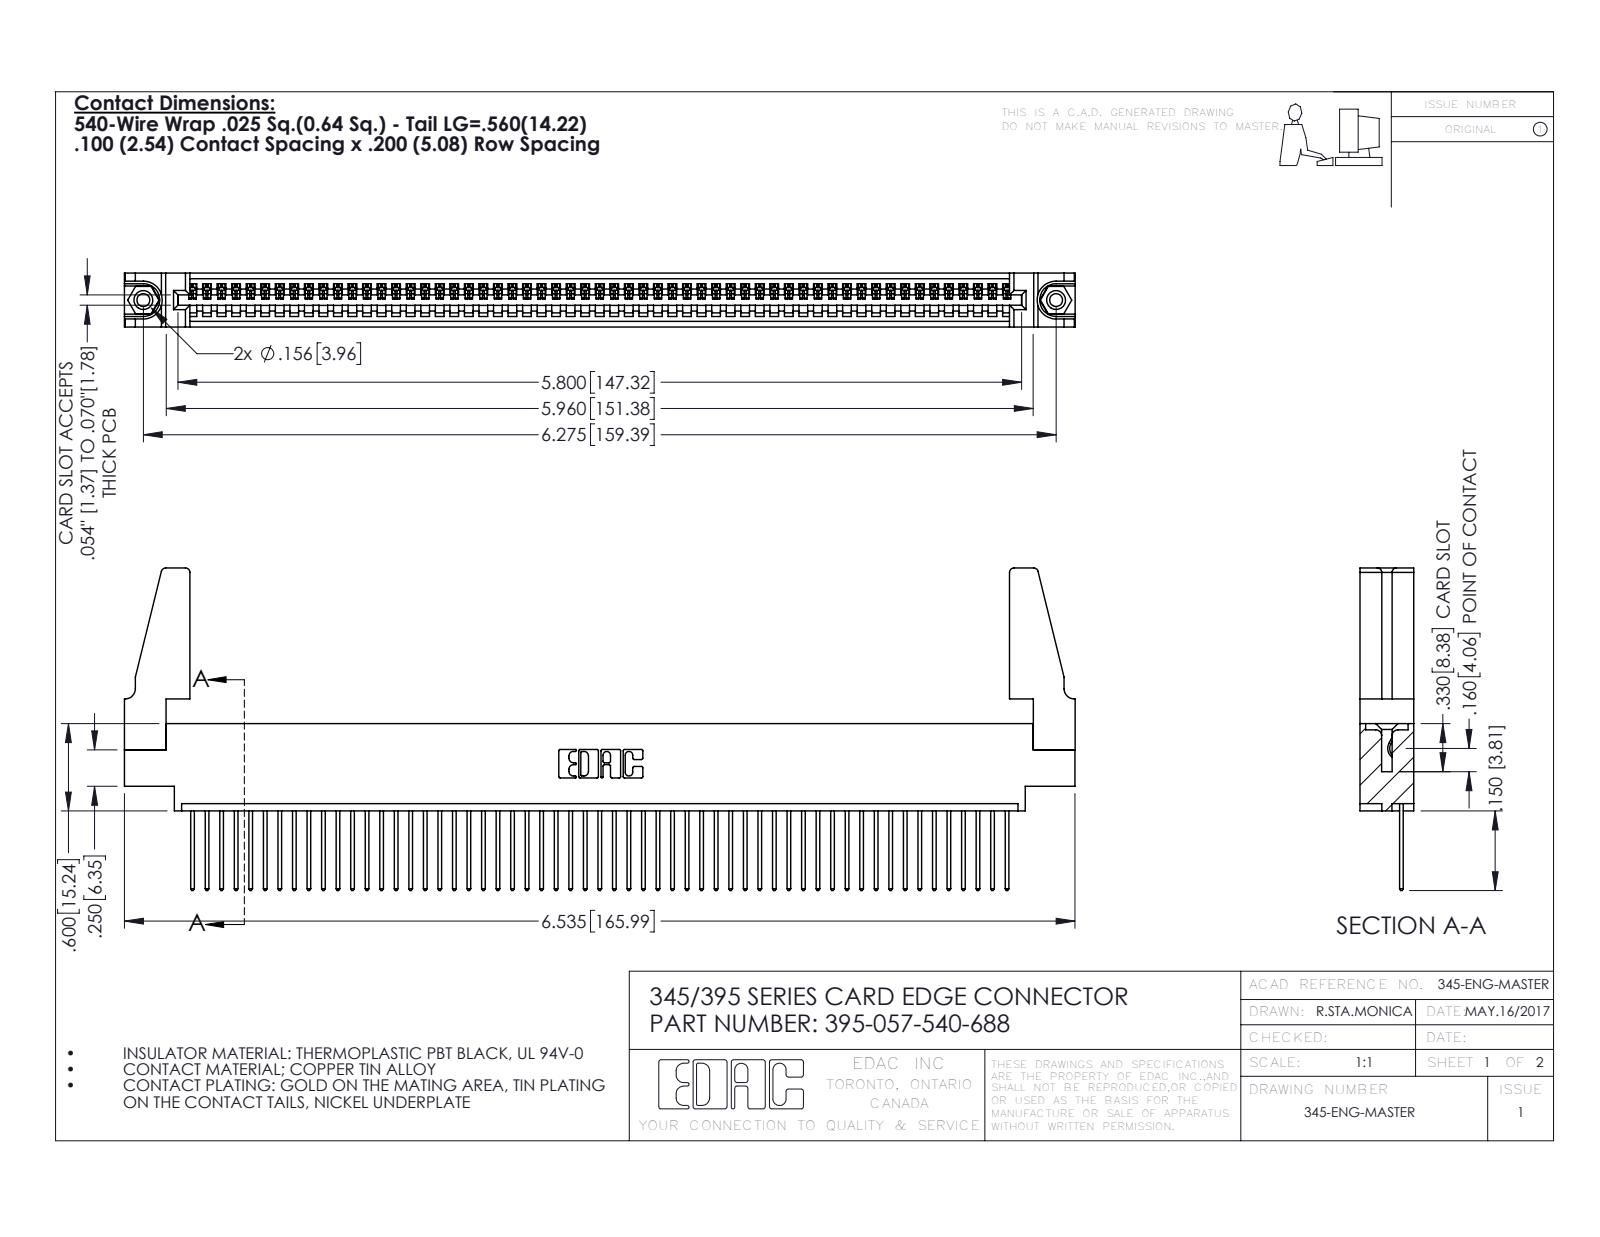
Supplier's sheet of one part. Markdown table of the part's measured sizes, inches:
| quantity | value |
| --- | --- |
| part name | 395-057-540-688; 345-220-078_345-220-088; 345 Part_0.170 Offset - 0.156 Dia-TH; 345-250-001_345-250-001-102 (+1 more) |
| STEP written by | SolidWorks 2016 (CONFIG_CONTROL_DESIGN) |
| units | inches |
| bodies | 62 solids, 3560 faces (2436 planar, 1108 cylindrical, 16 other) |
| overall size | 6.536 × 2.217 × 0.37 |
| volume | 1.166 in³ |
| surface area | 38.88 in² |
| round holes (diameter × count) | 0.089 × 2, 0.125 × 2, 0.156 × 2, 0.064 × 1 |
| round bosses / shafts (diameter × count) | 0.155 × 2 |
| partial cylindrical surfaces (radius × count) | 0.006 × 114, 0.01 × 114, 0.01 × 22, 0.03 × 8, 0.007 × 6, 0.031 × 6, 0.026 × 3, 0.031 × 2 |
| main face-to-face distances | 0.072, 0.298, 0.37, 0.098, 0.272, 0.025, 0.2, 0.225, 0.175, 0.149 |
| hole center spacings | 0.27, 6.039, 6.275 |
